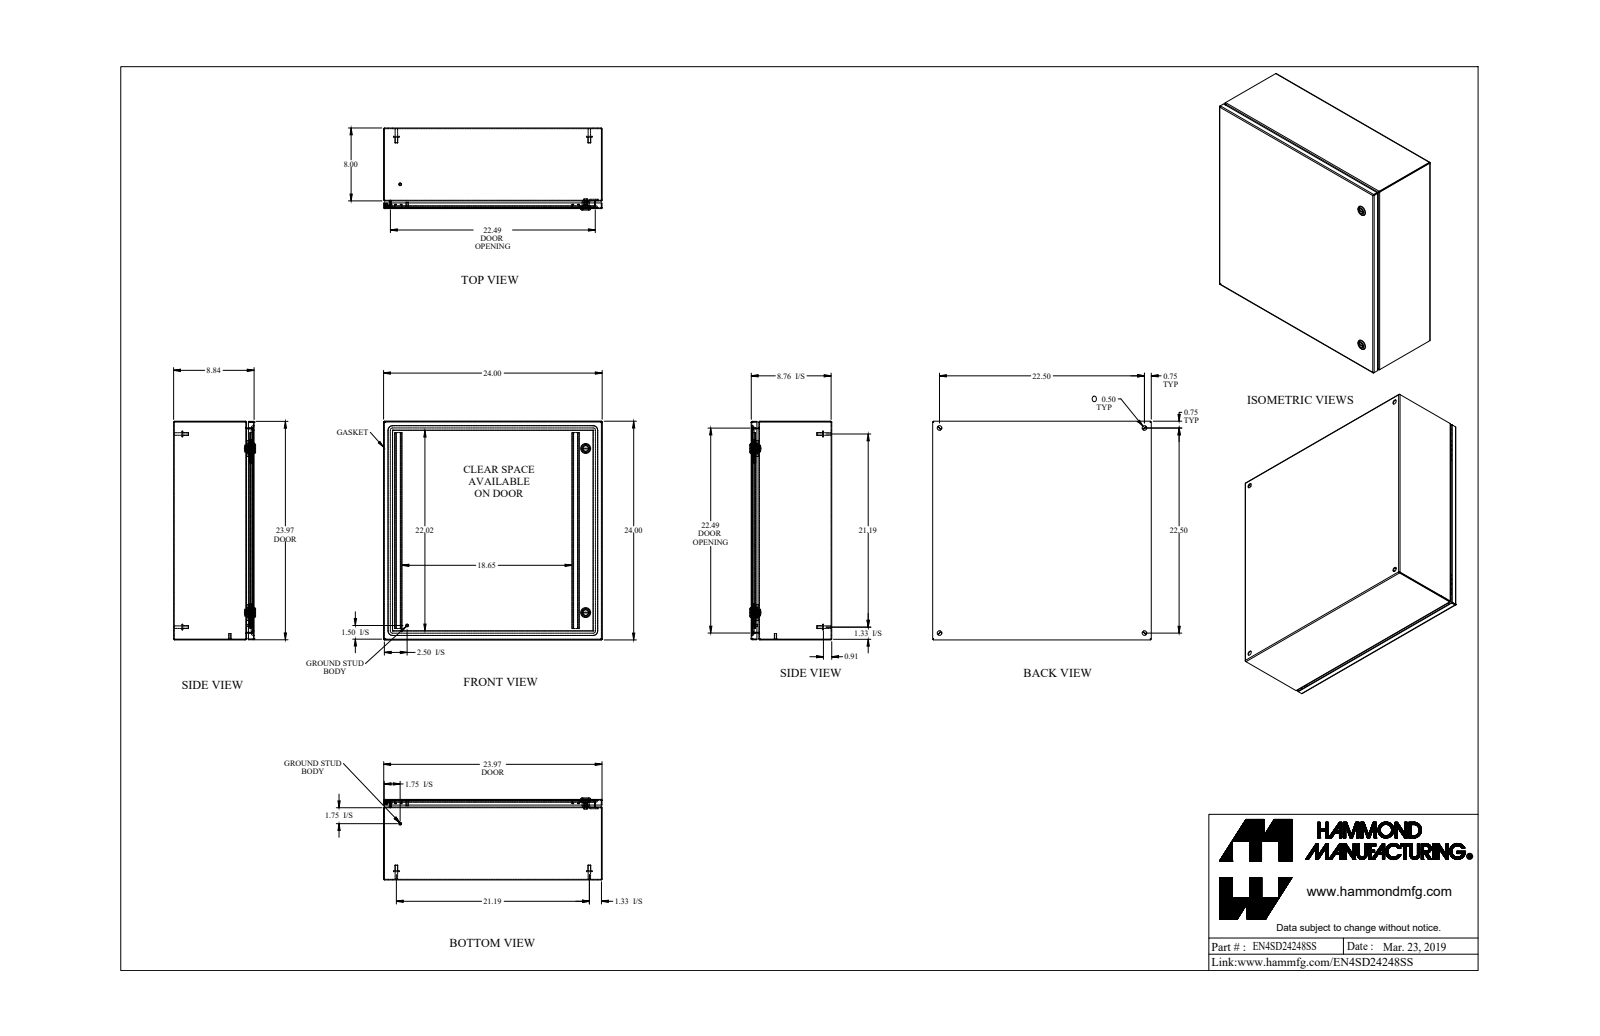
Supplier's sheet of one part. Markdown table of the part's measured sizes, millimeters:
| quantity | value |
| --- | --- |
| part name | EN4SD24248SS_Default |
| STEP written by | SolidWorks 2019 (CONFIG_CONTROL_DESIGN) |
| units | millimeters |
| bodies | 29 solids, 821 faces (414 planar, 263 cylindrical, 144 other) |
| overall size | 609.6 × 609.6 × 228.7 |
| volume | 2 687 000 mm³ |
| surface area | 2 966 000 mm² |
| round holes (diameter × count) | 12.7 × 6, 5 × 2, 9.8 × 2, 16 × 2, 19.5 × 2, 4.4 × 1, 6.1 × 1, 6.1 × 1 |
| round bosses / shafts (diameter × count) | 15.9 × 6, 8 × 6, 7 × 4, 27.9 × 2, 19.9 × 2, 13.3 × 2, 6.4 × 2, 6 × 2 |
| partial cylindrical surfaces (radius × count) | 0.9 × 20, 2.7 × 20, 6.4 × 16, 0.3 × 12, 1.2 × 12, 0.2 × 4, 1.6 × 4, 3.2 × 4 |
| main face-to-face distances | 1.8, 222.8, 607.8, 220.9, 224.6, 605.9, 609.6, 21.4, 201.4, 19.1 |
| hole center spacings | 571.5, 63.2, 515.1, 547.5, 749.1, 808.2, 457.2 |
